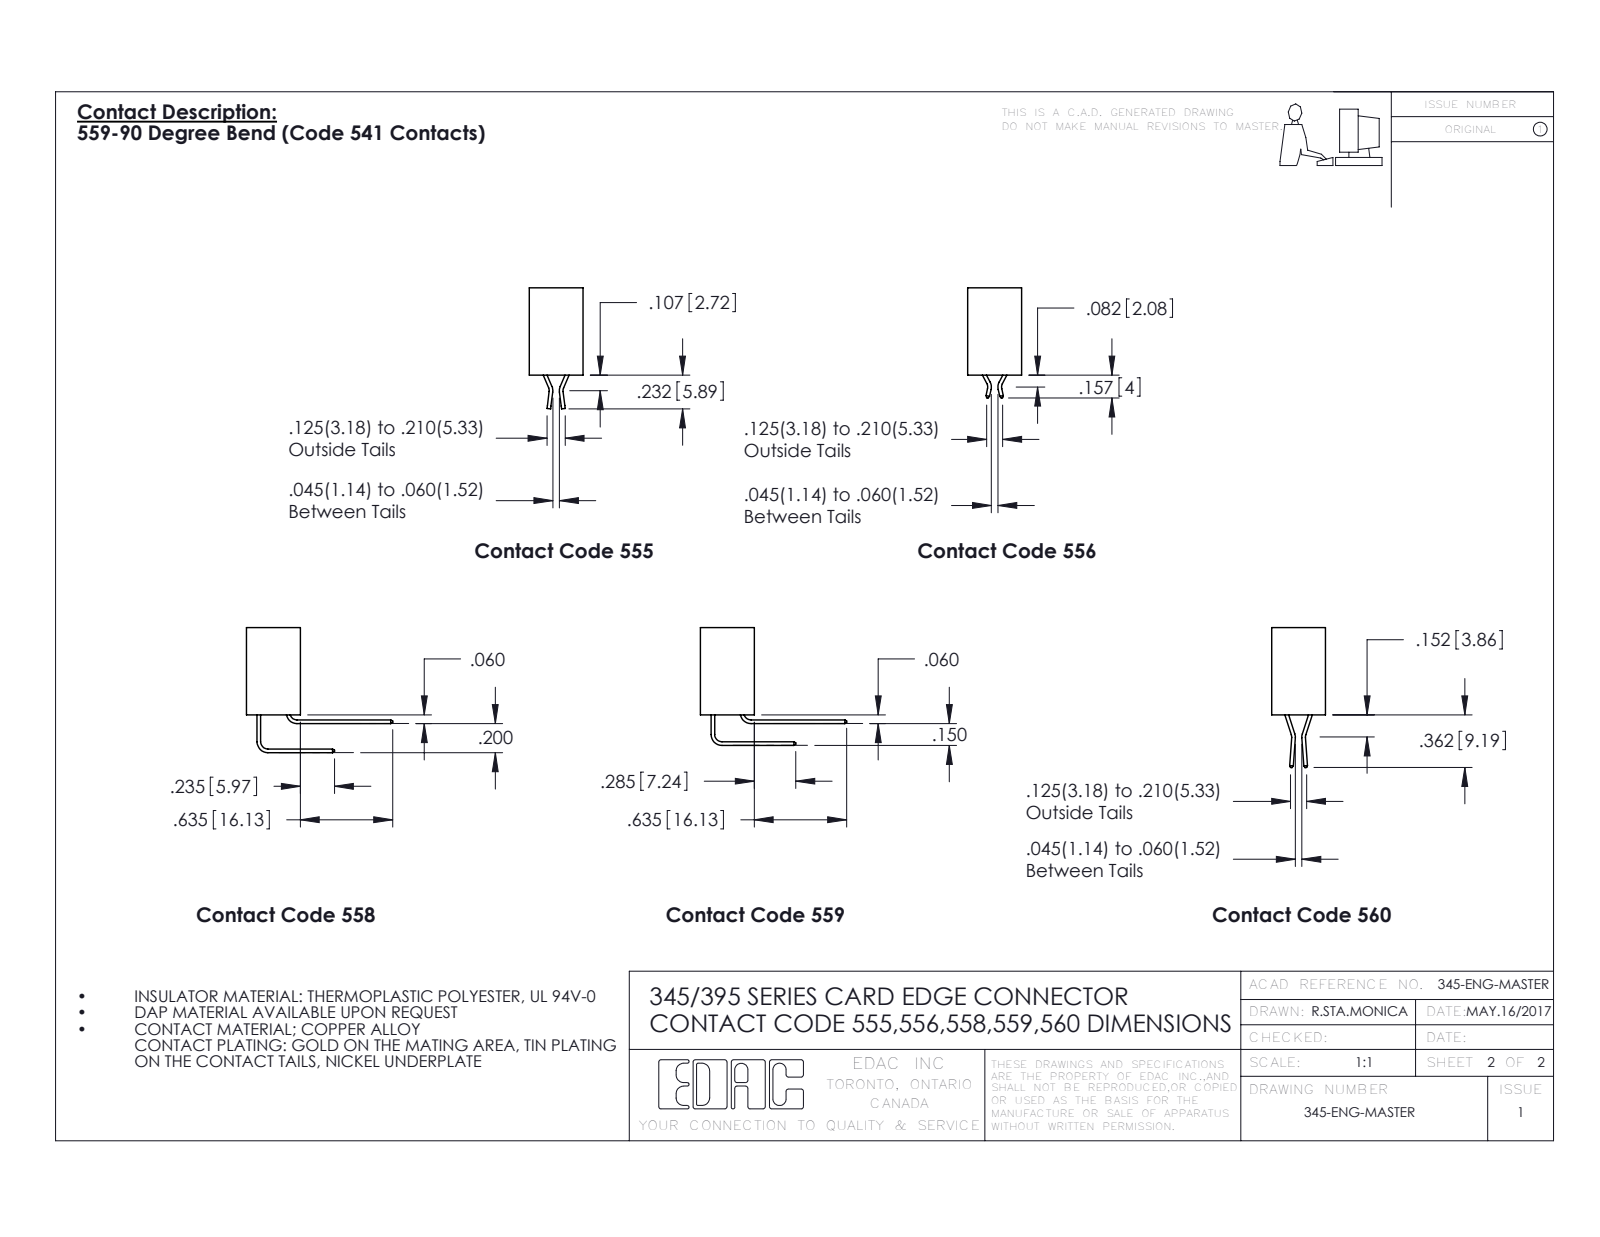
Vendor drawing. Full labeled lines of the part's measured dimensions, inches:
Part name (STEP PRODUCT): 395-118-558-201; 345 Part_No Mounting Lugs; 345-292-001_558 Tail - 2; 345-292-001_558 559 Tail - 1
STEP written by: SolidWorks 2016 (CONFIG_CONTROL_DESIGN)
Units: inches
Bodies: 119 solids, 6254 faces (4206 planar, 2048 cylindrical, 0 other)
Overall size (bounding box): 6.16 × 1.005 × 0.859
Volume: 1.016 in³ · Surface area: 44.1 in²
Round holes (diameter × count): ⌀0.064 ×1
Partial cylindrical surfaces — rounded edges, fillets, slot ends (radius × count): R0.006 ×178, R0.01 ×22, R0.007 ×6, R0.031 ×6, R0.026 ×3, R0.014 ×2, R0.019 ×2, R0.022 ×2
Main face-to-face distances: 0.072, 0.298, 0.2, 0.098, 0.272, 0.025, 0.37, 0.225, 0.025, 0.175
